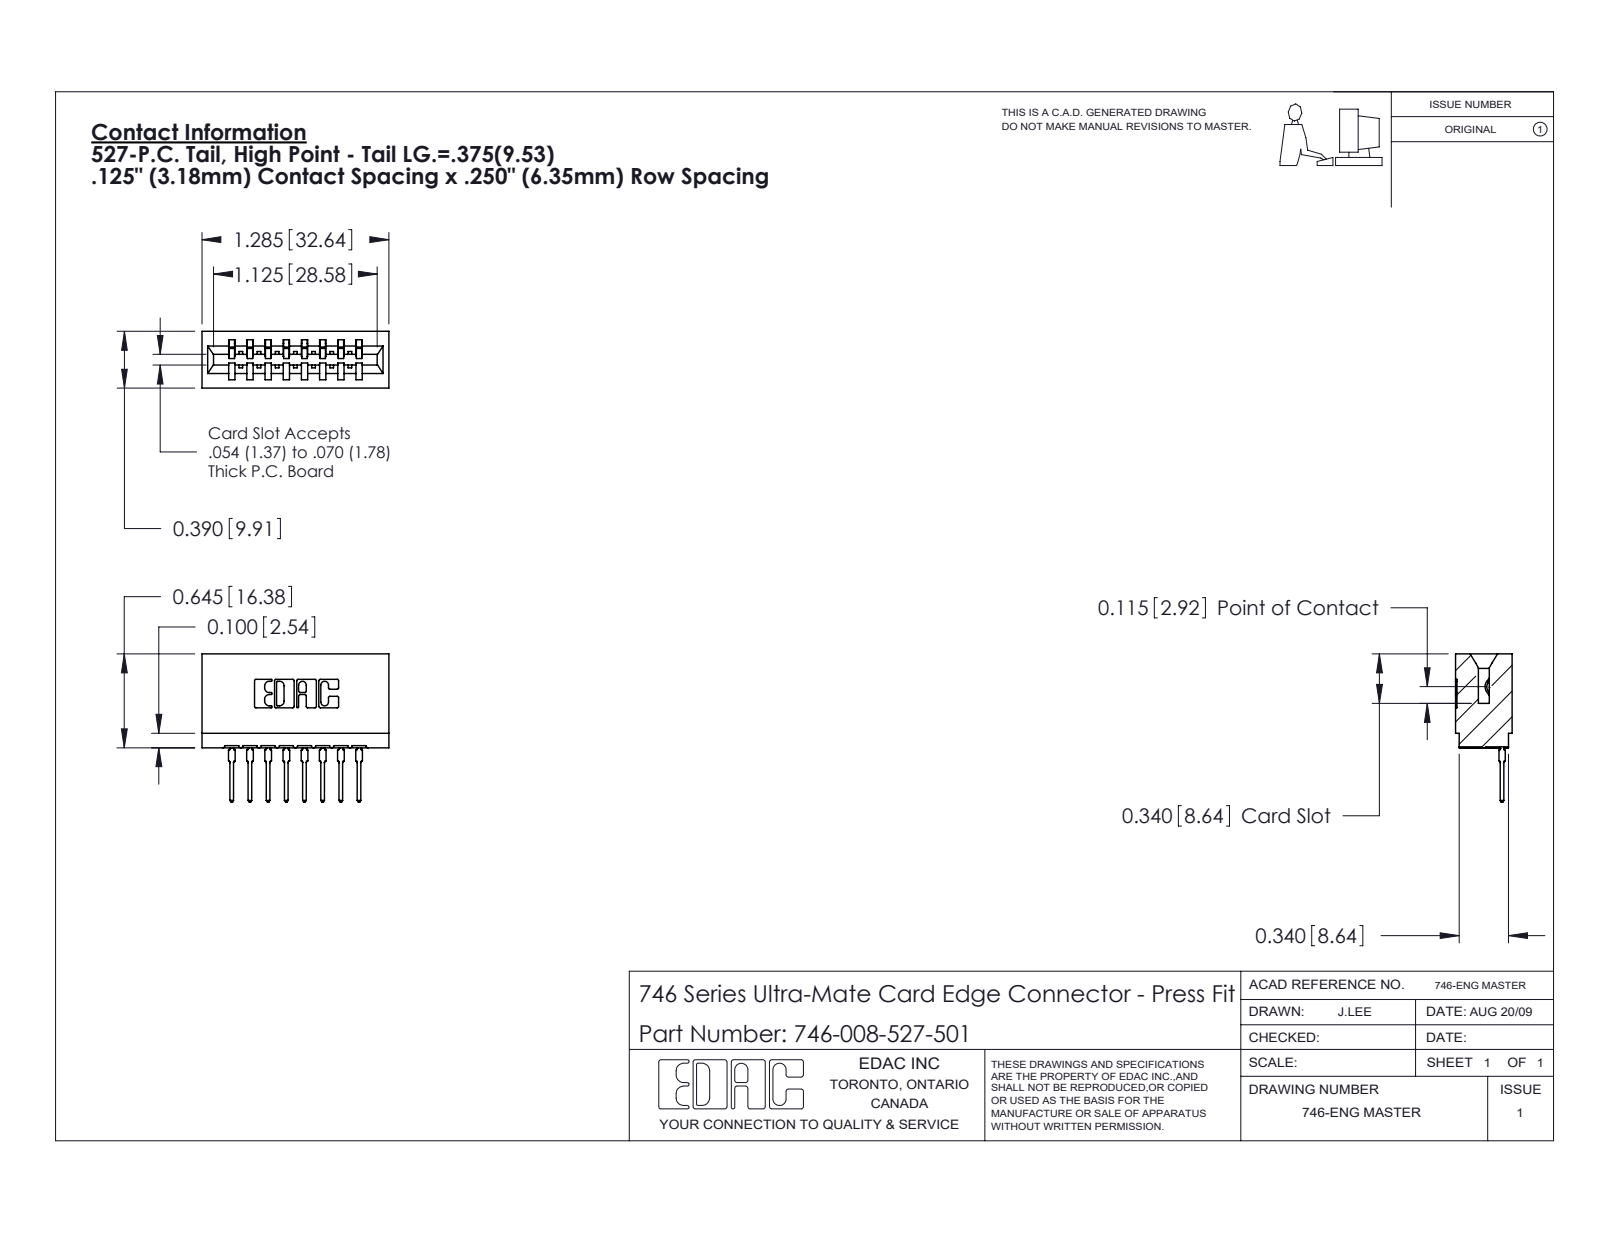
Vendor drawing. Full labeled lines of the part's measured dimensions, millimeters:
Part name (STEP PRODUCT): 746-292-001_527; 746-008-527-501; 746 Part_.340 Slot Depth - 01
STEP written by: SolidWorks 2020 (CONFIG_CONTROL_DESIGN)
Units: millimetres
Bodies: 9 solids, 961 faces (559 planar, 194 cylindrical, 208 other)
Overall size (bounding box): 32.6 × 25.9 × 9.9
Volume: 3 880 mm³ · Surface area: 4 759 mm²
Partial cylindrical surfaces — rounded edges, fillets, slot ends (radius × count): R0.3 ×22, R0.5 ×16, R0.4 ×9, R0.2 ×6, R0.8 ×6, R0.1 ×4, R0.3 ×4, R0.7 ×3
Main face-to-face distances: 6.4, 1.1, 3.2, 12.7, 8.5, 1.4, 7.4, 9.5, 5.3, 3.2
